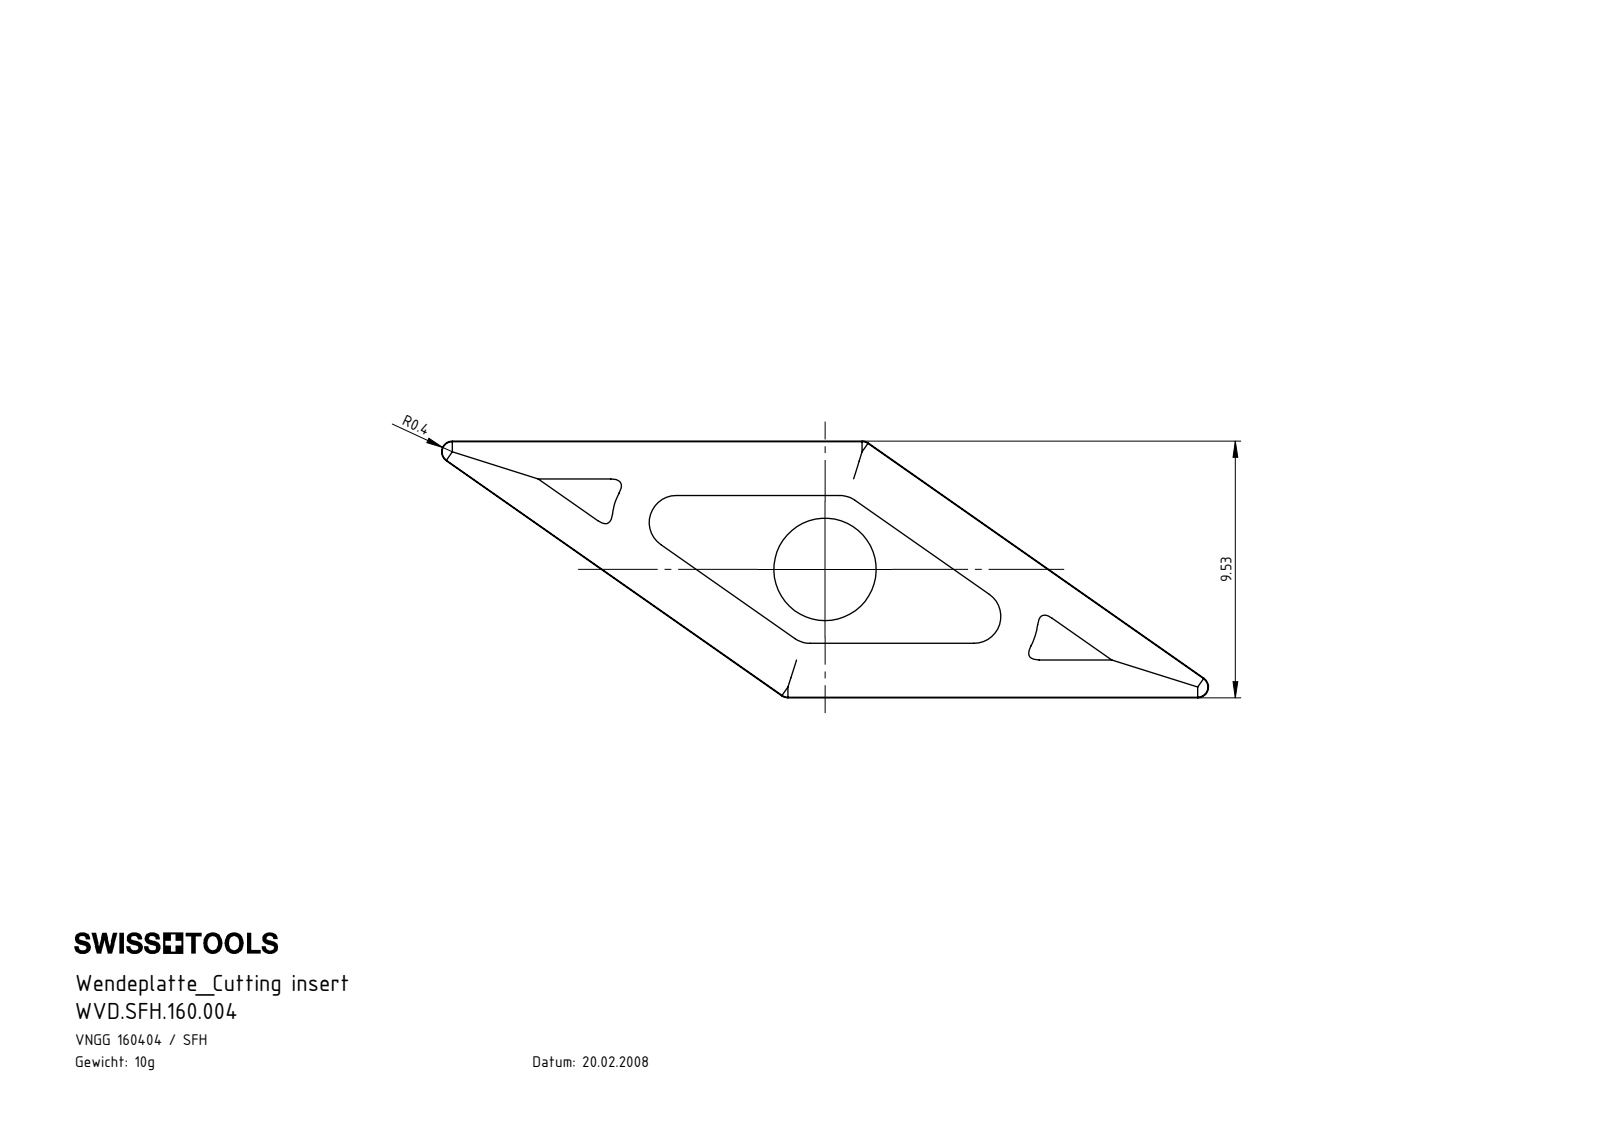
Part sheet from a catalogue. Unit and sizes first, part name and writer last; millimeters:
Units: millimetres
Overall size (bounding box): 28.47 × 9.53 × 4.76
Round holes (diameter × count): ⌀3.8 ×1
Partial cylindrical surfaces — rounded edges, fillets, slot ends (radius × count): R0.4 ×4
Main face-to-face distances: 9.52, 9.54, 4.76, 3.74, 3.96, 0.8
Volume: 659 mm³ · Surface area: 664 mm²
Bodies: 1 solid, 43 faces (17 planar, 6 cylindrical, 20 other)
Part name (STEP PRODUCT): WVD.SFH.160.004
STEP written by: SolidWorks 2022 (AUTOMOTIVE_DESIGN)
